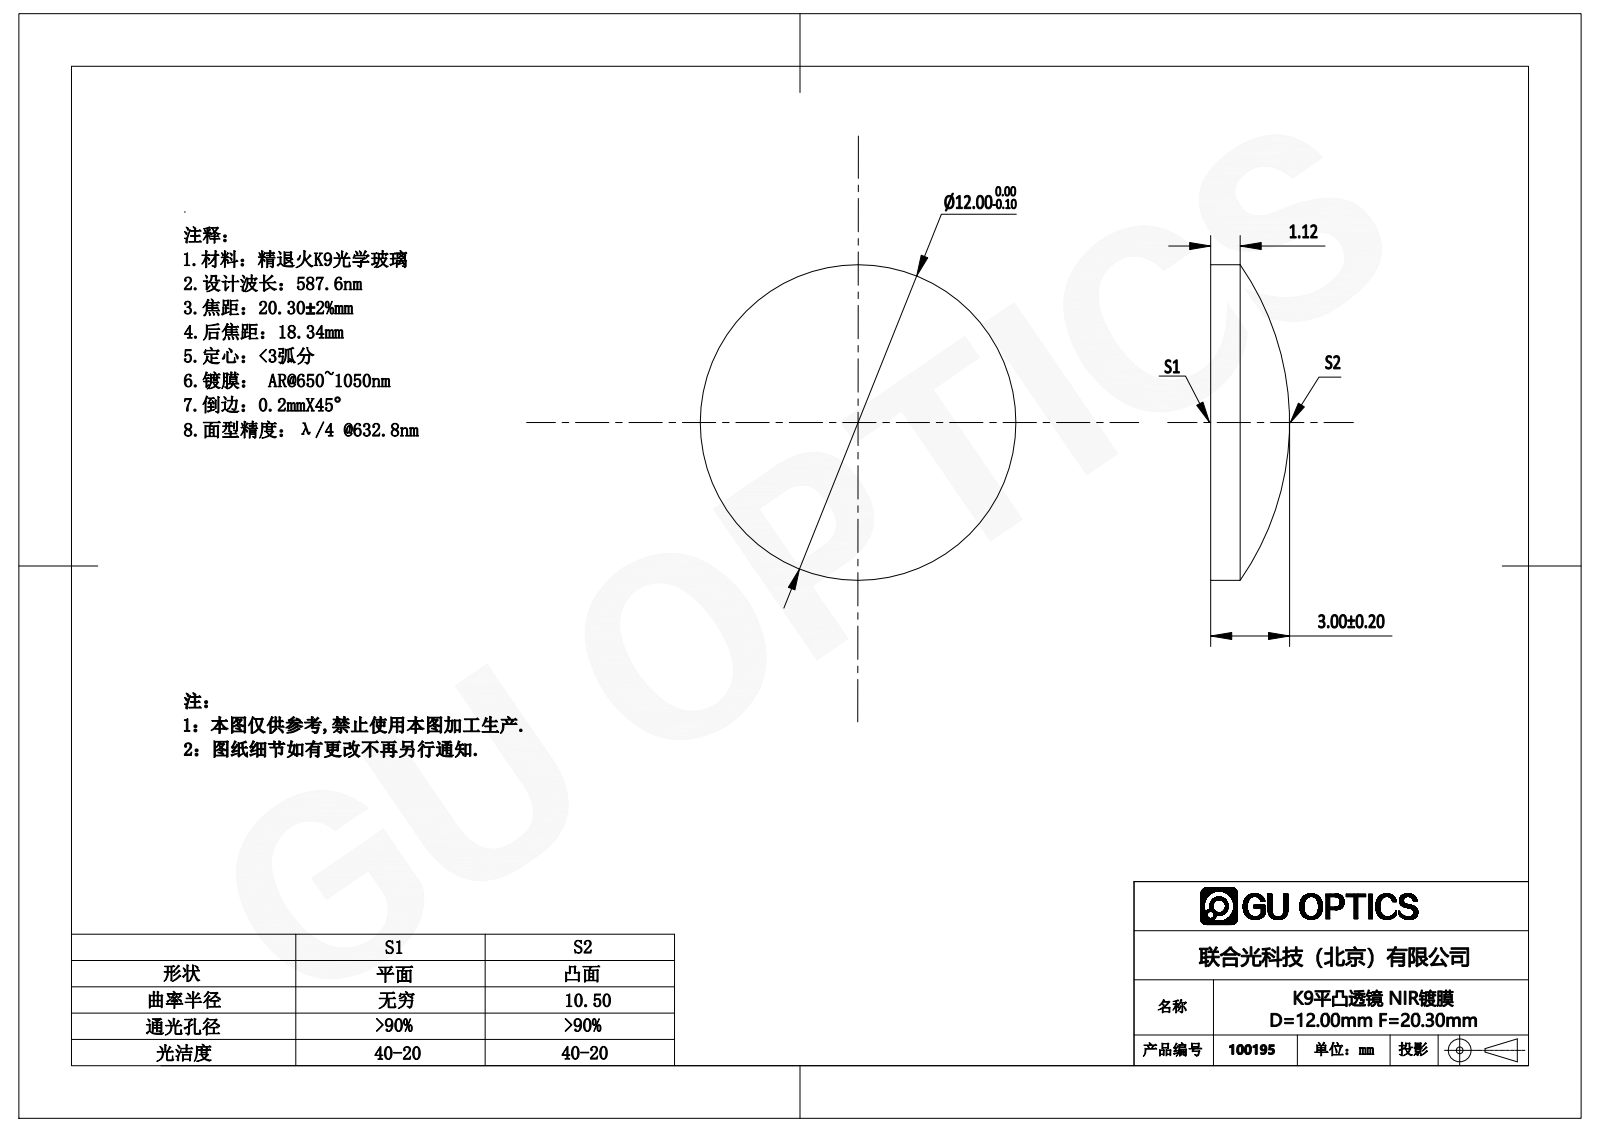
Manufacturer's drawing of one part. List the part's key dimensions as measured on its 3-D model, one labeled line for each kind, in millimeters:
Part name (STEP PRODUCT): 100195
STEP written by: SolidWorks 2016 (AUTOMOTIVE_DESIGN)
Units: millimetres
Bodies: 1 solid, 5 faces (1 planar, 2 cylindrical, 2 other)
Overall size (bounding box): 12 × 12 × 3
Volume: 236 mm³ · Surface area: 280 mm²
Round bosses / shafts (diameter × count): ⌀12 ×1
